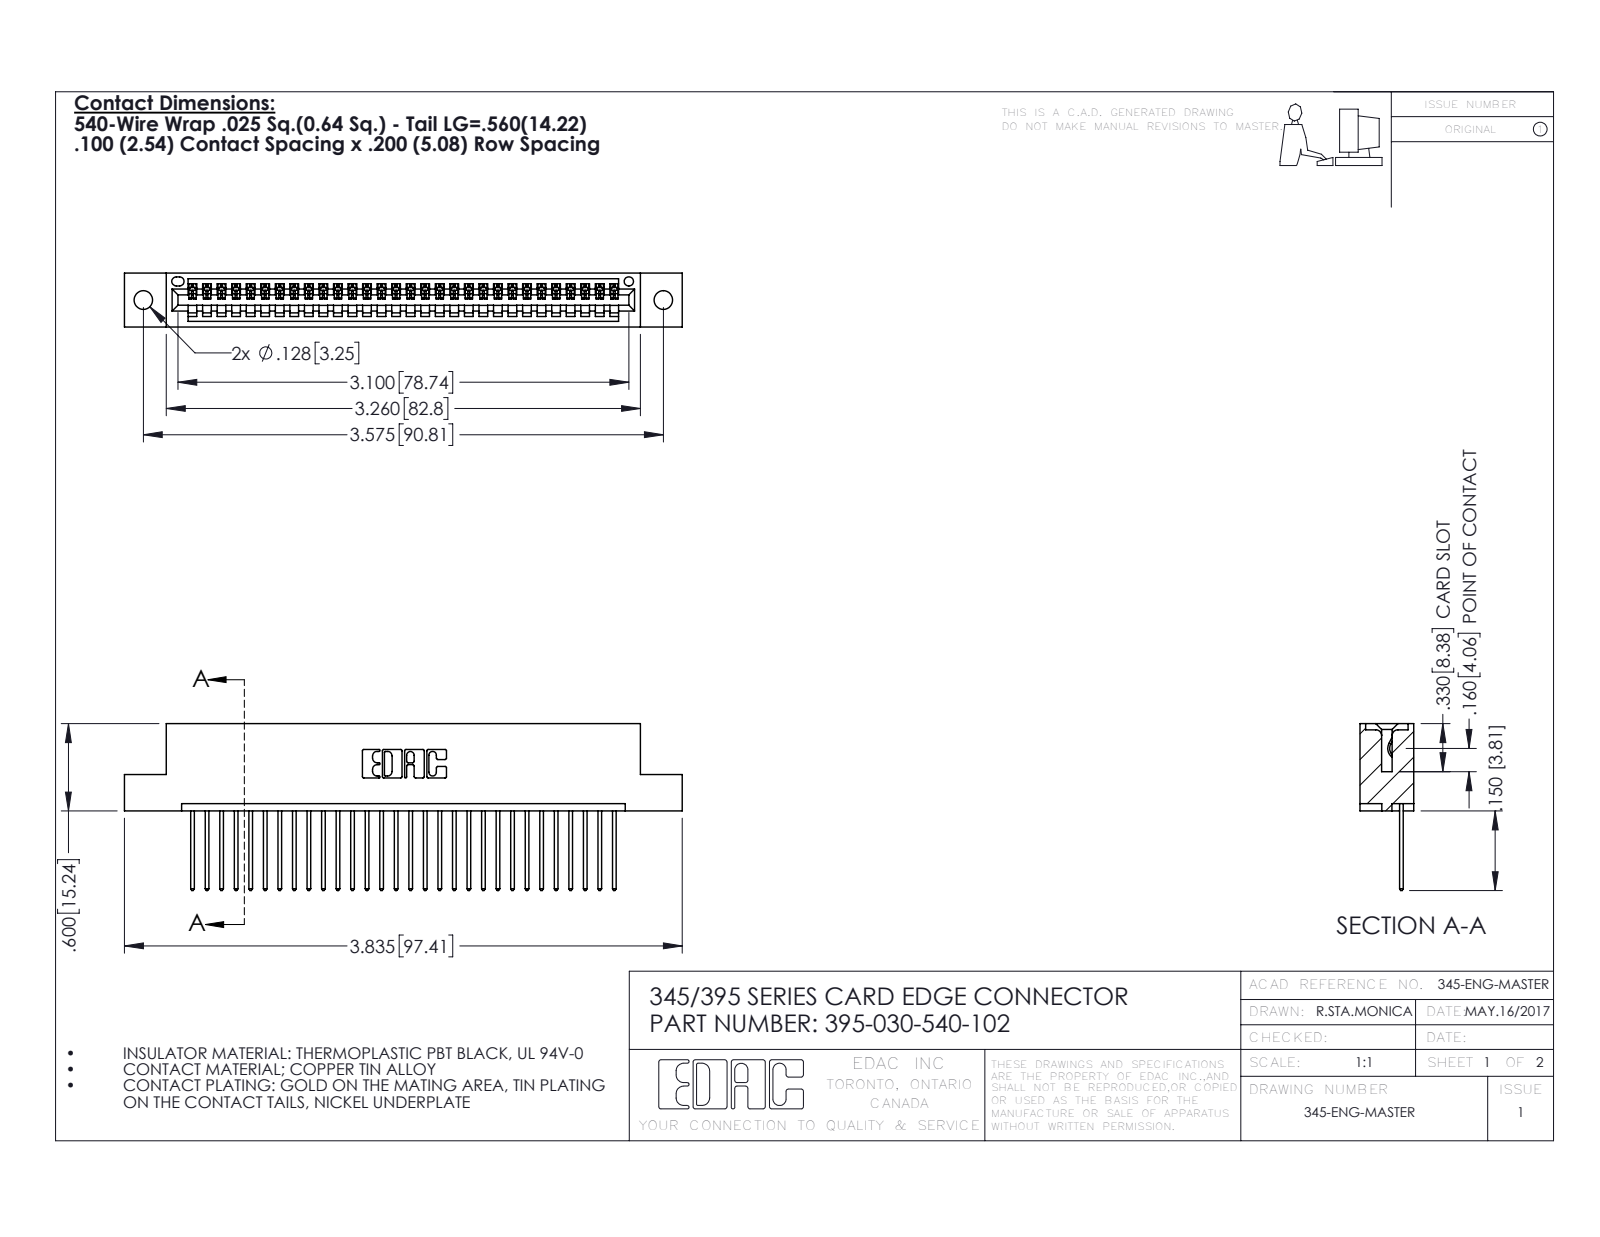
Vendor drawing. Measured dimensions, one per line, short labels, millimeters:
name: 345 Part_Flush Mounting Lugs - 0.128 Dia; 345-292-001_345-293-140; 395-030-540-102
written by: SolidWorks 2016 (CONFIG_CONTROL_DESIGN)
unit: mm
bodies: 31 solids, 1866 faces (1280 planar, 586 cylindrical, 0 other)
size: 97.4 × 29.1 × 9.4
volume: 9 160 mm³; area: 12 030 mm²
holes: 2× ⌀3.3, 1× ⌀1.6
rounds: 60× R0.2, 60× R0.3, 22× R0.3, 6× R0.2, 6× R0.8, 3× R0.7, 2× R0.8, 2× R1
face distances: 7.6, 1.8, 5.1, 9.4, 2.5, 6.9, 0.6, 5.7, 3.8, 1.8
hole spacings: 6.9, 84.8, 90.8
